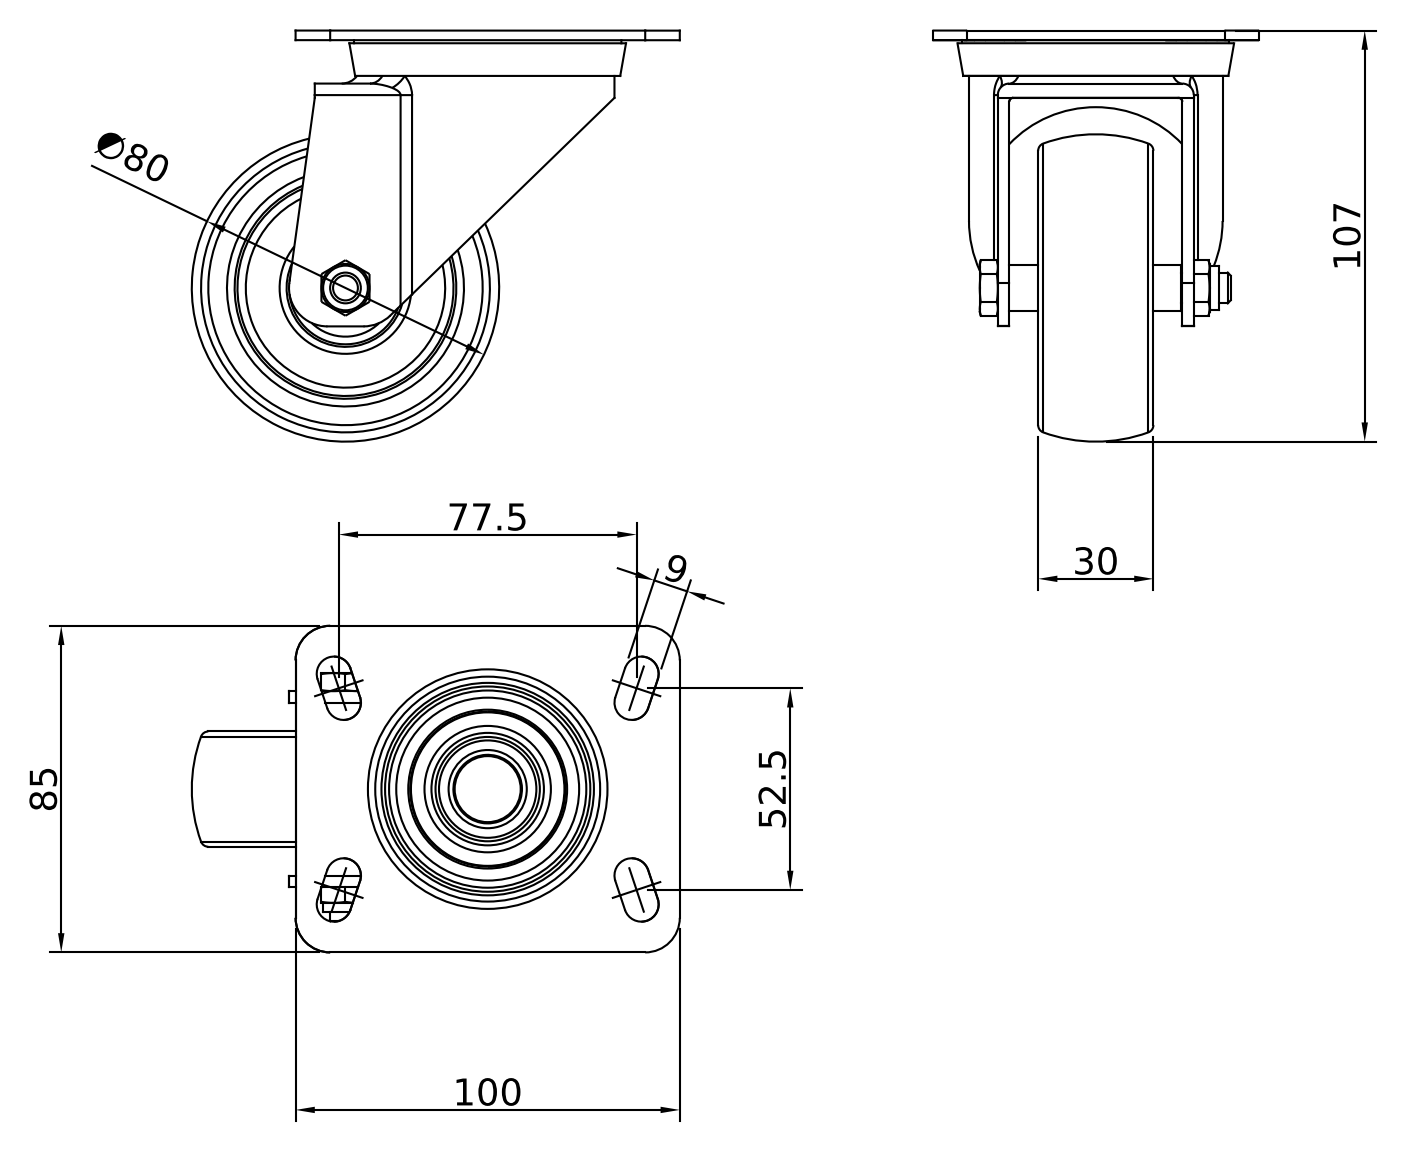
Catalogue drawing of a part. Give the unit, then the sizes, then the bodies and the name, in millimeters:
Units: millimetres
Overall size (bounding box): 127.01 × 107 × 85
Round holes (diameter × count): ⌀9 ×1, ⌀40.35 ×1, ⌀61 ×1
Round bosses / shafts (diameter × count): ⌀69.6 ×1, ⌀12 ×1, ⌀11.63 ×1, ⌀8 ×1
Partial cylindrical surfaces — rounded edges, fillets, slot ends (radius × count): R4.5 ×8, R9 ×4, R1 ×2, R3 ×2, R5 ×2, R10 ×2, R33 ×1
Main face-to-face distances: 2.5, 10.5, 11.51, 14.01, 3, 7.5, 48, 37.5, 40.5, 45
Volume: 177 012 mm³ · Surface area: 59 845 mm²
Bodies: 1 solid, 145 faces (57 planar, 34 cylindrical, 54 other)
Part name (STEP PRODUCT): CRUST0000062
STEP written by: Autodesk Inventor 2022 (AUTOMOTIVE_DESIGN)
